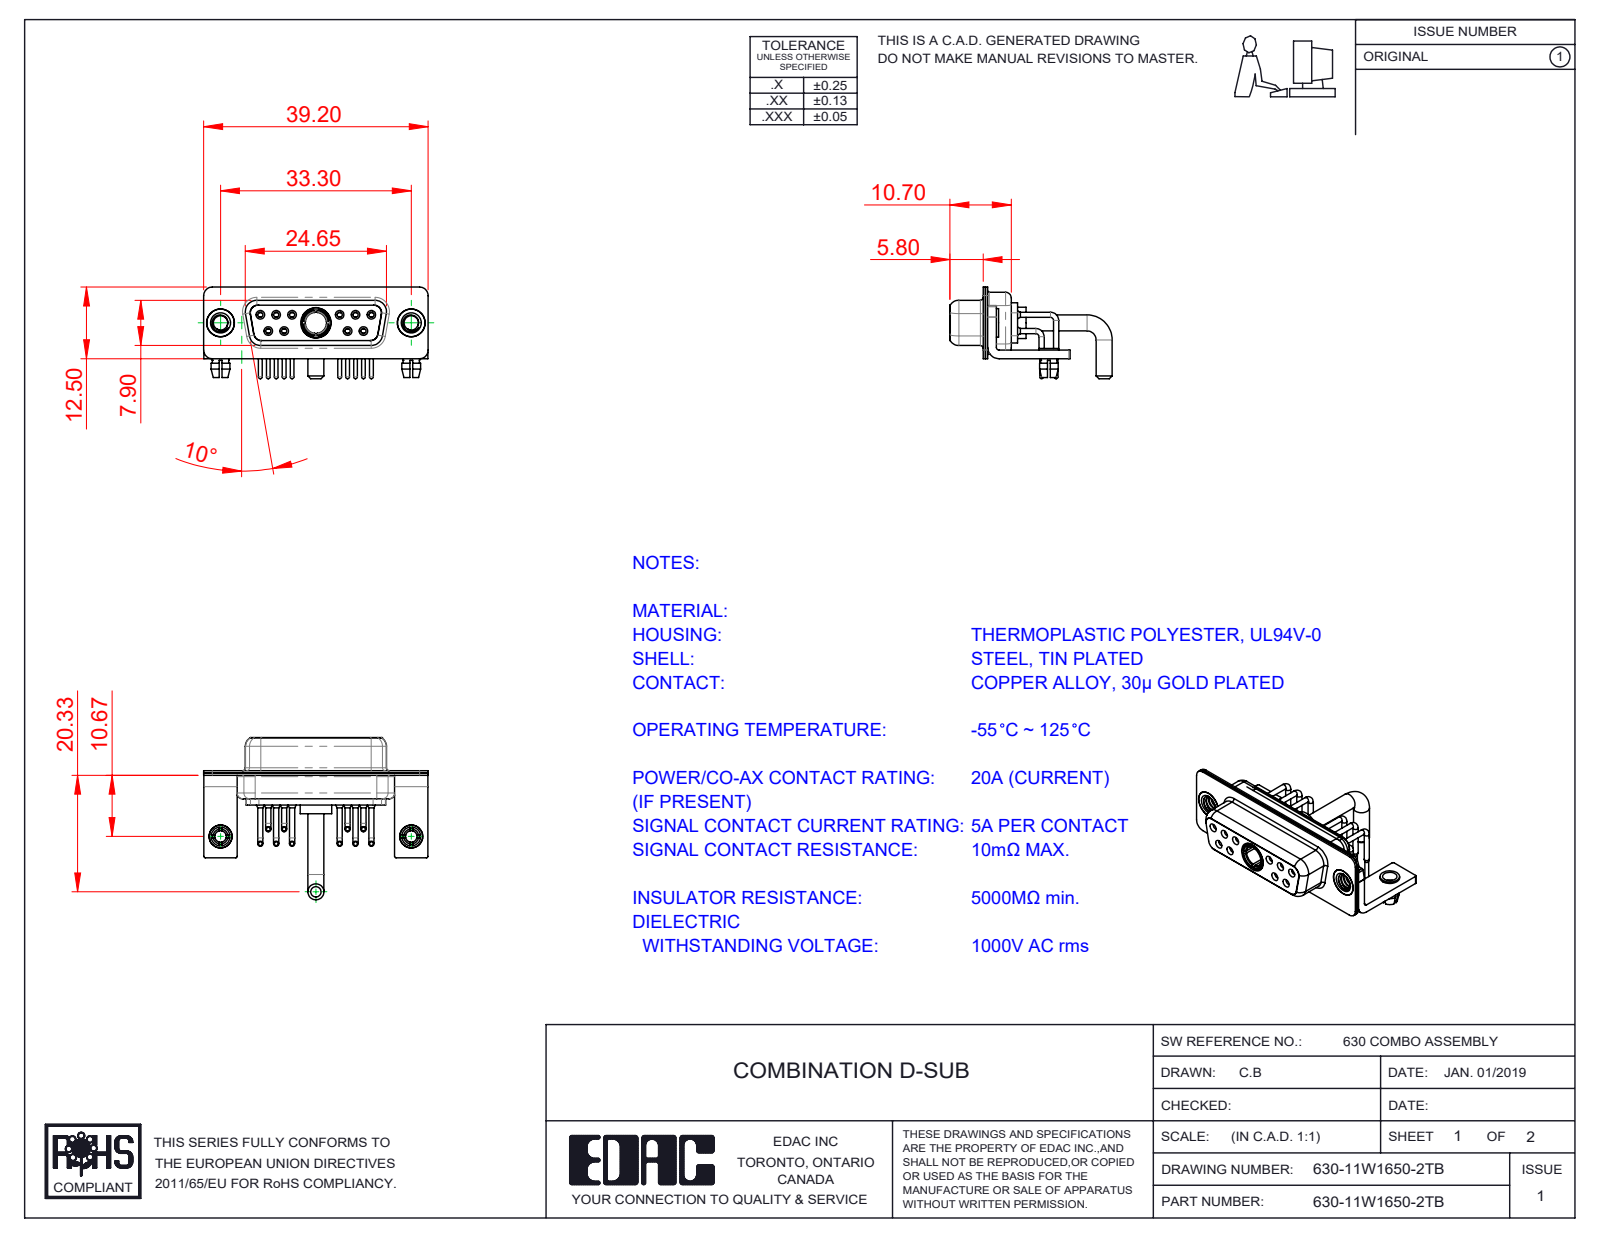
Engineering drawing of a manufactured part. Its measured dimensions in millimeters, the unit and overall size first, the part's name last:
Units: millimetres
Overall size (bounding box): 39.2 × 28.33 × 16
Round holes (diameter × count): ⌀2 ×12, ⌀0.9 ×10, ⌀1.1 ×10, ⌀1.5 ×10, ⌀1.7 ×6, ⌀1.6 ×4, ⌀2.5 ×4, ⌀4.85 ×3, ⌀3.2 ×2, ⌀4 ×2, ⌀4.05 ×2, ⌀3.7 ×1
Round bosses / shafts (diameter × count): ⌀0.9 ×10, ⌀0.65 ×10, ⌀1.6 ×6, ⌀5 ×2, ⌀4.95 ×2, ⌀4.8 ×2, ⌀4 ×2, ⌀3.4 ×2
Partial cylindrical surfaces — rounded edges, fillets, slot ends (radius × count): R0.25 ×16, R1.5 ×16, R2 ×13, R1.35 ×12, R1.6 ×8, R0.5 ×5, R0.6 ×4, R0.65 ×4
Main face-to-face distances: 0.4, 0.8, 0.45, 1.4, 8.45, 1.5, 1.8, 8.9, 6.2, 2.3
Hole centre spacings: 3.16, 2.77, 13.85, 11.08, 16.62, 5.03, 5.04, 5.54
Volume: 2 988 mm³ · Surface area: 7 133 mm²
Bodies: 21 solids, 1017 faces (314 planar, 442 cylindrical, 261 other)
Part name (STEP PRODUCT): 630Combo Board Lock; 630Combo Shell Rear_15 Contacts; 630Combo Contact Row 2; 630Combo Housing_11W1 (+6 more)
STEP written by: SolidWorks 2020 (CONFIG_CONTROL_DESIGN)
